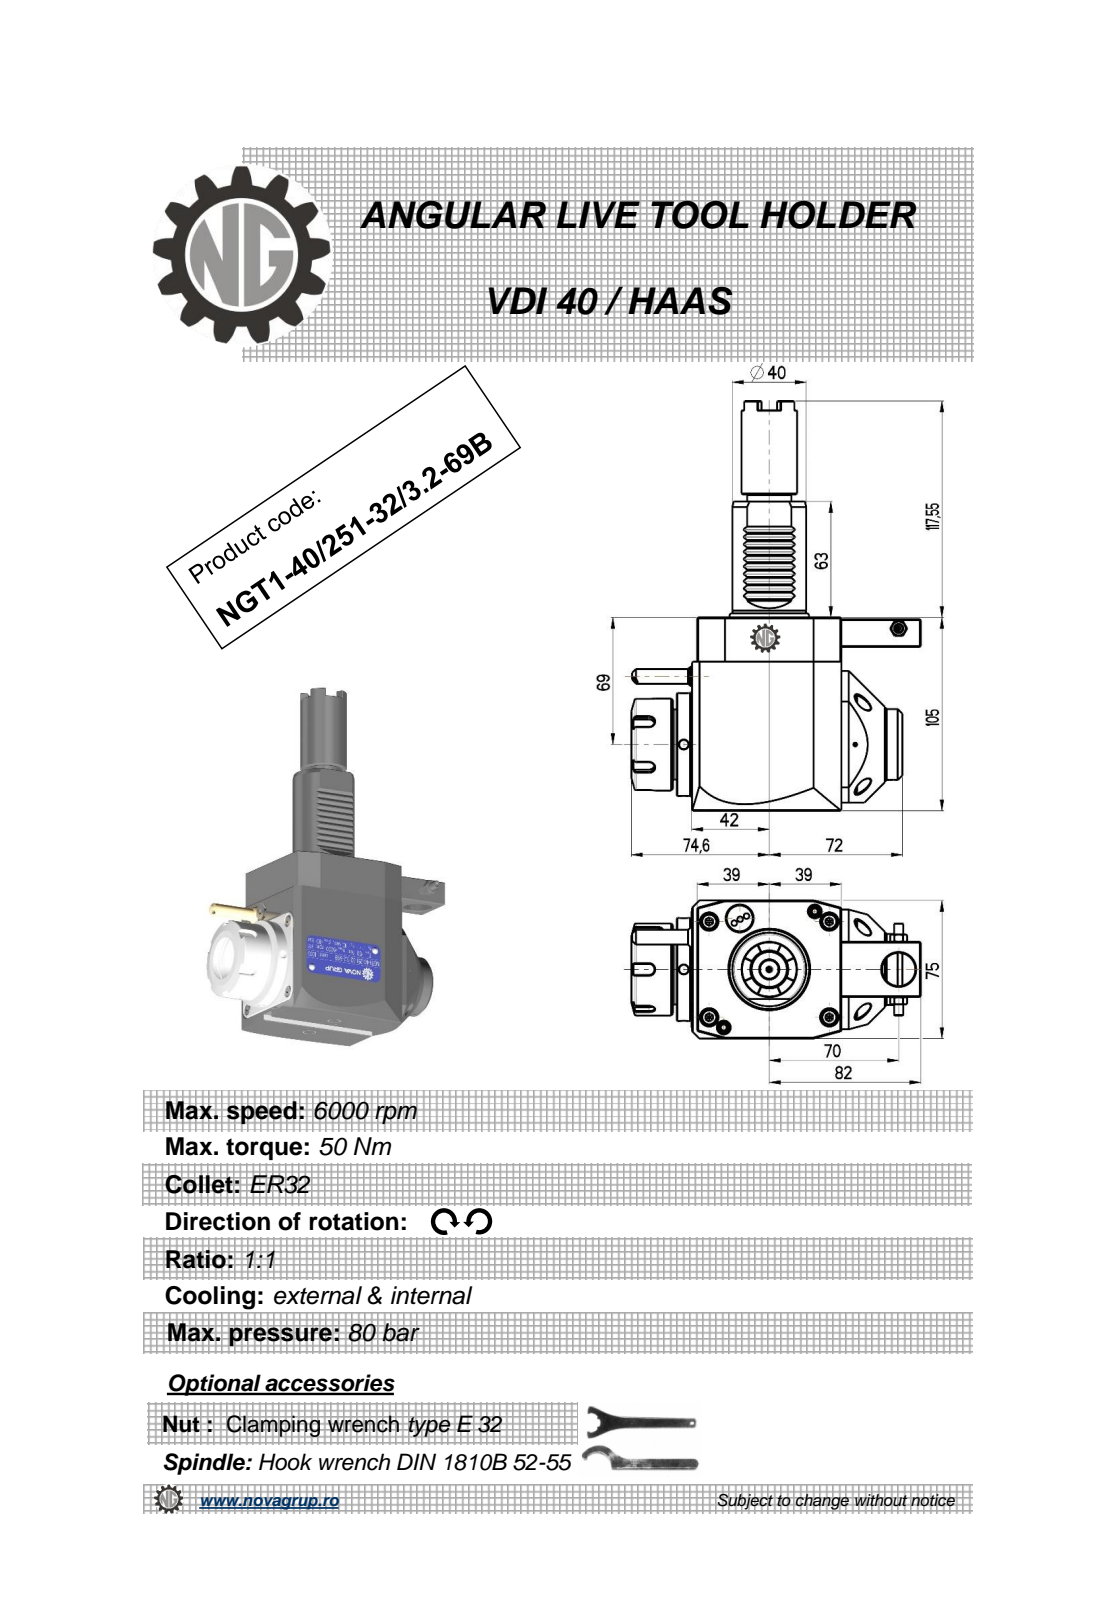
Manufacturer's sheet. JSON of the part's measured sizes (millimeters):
{"part_name": "NGT1_40_251_32_3_2_69B", "step_written_by": "PRO/ENGINEER BY PARAMETRIC TECHNOLOGY CORPORATION, 2010280 (CONFIG_CONTROL_DESIGN)", "units": "millimeters", "bodies": {"solids": 1, "faces": 453, "planar": 216, "cylindrical": 91, "other": 146}, "overall_size": [222.55, 156.6, 75], "volume_mm3": 888123, "surface_area_mm2": 76455, "round_holes": [[5, 3], [3, 1], [4.2, 1], [9.5, 1], [18, 1], [27, 1]], "round_bosses_or_shafts": [[56, 1], [50, 1], [43, 1], [40, 1], [38.5, 1], [30, 1], [24, 1], [10, 1]], "partial_cylinders_radius": [[0.26, 12], [0.3, 10], [0.2, 6], [3, 5], [0.5, 1], [10, 1], [40, 1]], "face_to_face_distances": [75, 105, 81, 89, 1, 3, 2.8, 78, 80.8, 22.5], "hole_center_spacings": [30.11, 40.93, 61.5, 116.25, 132.22]}
